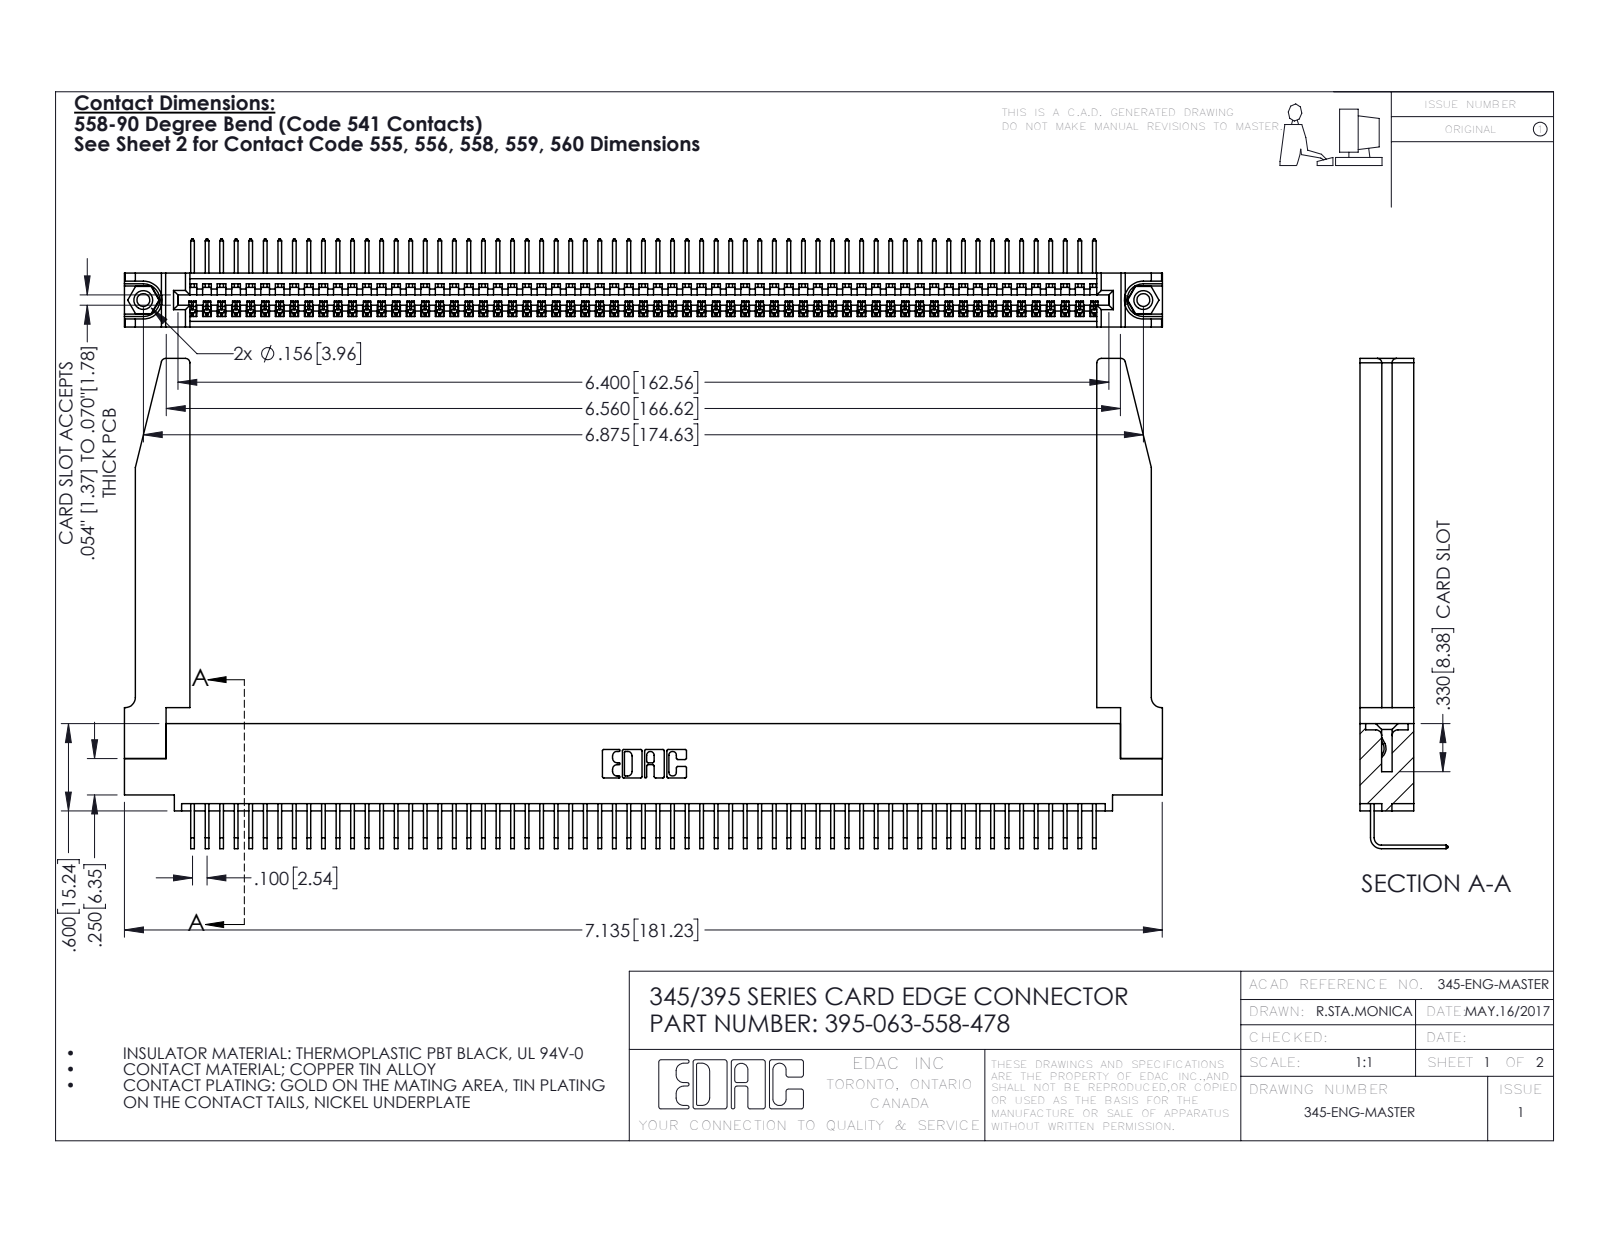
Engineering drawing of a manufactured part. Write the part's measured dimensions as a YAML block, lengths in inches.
part_name: "345-250-001_345-250-001-102; 345-220-078_345-220-078; 345 Part_0.110 Offset - 0.156 Dia-TH; 345-292-001_558 Tail - 2 (+1 more)"
step_written_by: "SolidWorks 2016 (CONFIG_CONTROL_DESIGN)"
units: inches
bodies: {solids: 68, faces: 4144, planar: 2872, cylindrical: 1220, other: 52}
overall_size: [7.136, 3.369, 0.605]
volume: 1.544
surface_area: 49.19
round_holes:
  - {diameter: 0.089, count: 2}
  - {diameter: 0.125, count: 2}
  - {diameter: 0.156, count: 2}
  - {diameter: 0.064, count: 1}
round_bosses_or_shafts:
  - {diameter: 0.155, count: 2}
partial_cylinders:
  - {radius: 0.006, count: 126}
  - {radius: 0.01, count: 22}
  - {radius: 0.03, count: 8}
  - {radius: 0.007, count: 6}
  - {radius: 0.031, count: 6}
  - {radius: 0.026, count: 3}
  - {radius: 0.031, count: 2}
  - {radius: 0.04, count: 2}
face_to_face_distances: [0.072, 0.37, 0.298, 0.2, 0.098, 0.272, 0.025, 0.225, 0.148, 0.15]
hole_center_spacings: [0.27, 6.639, 6.875]
